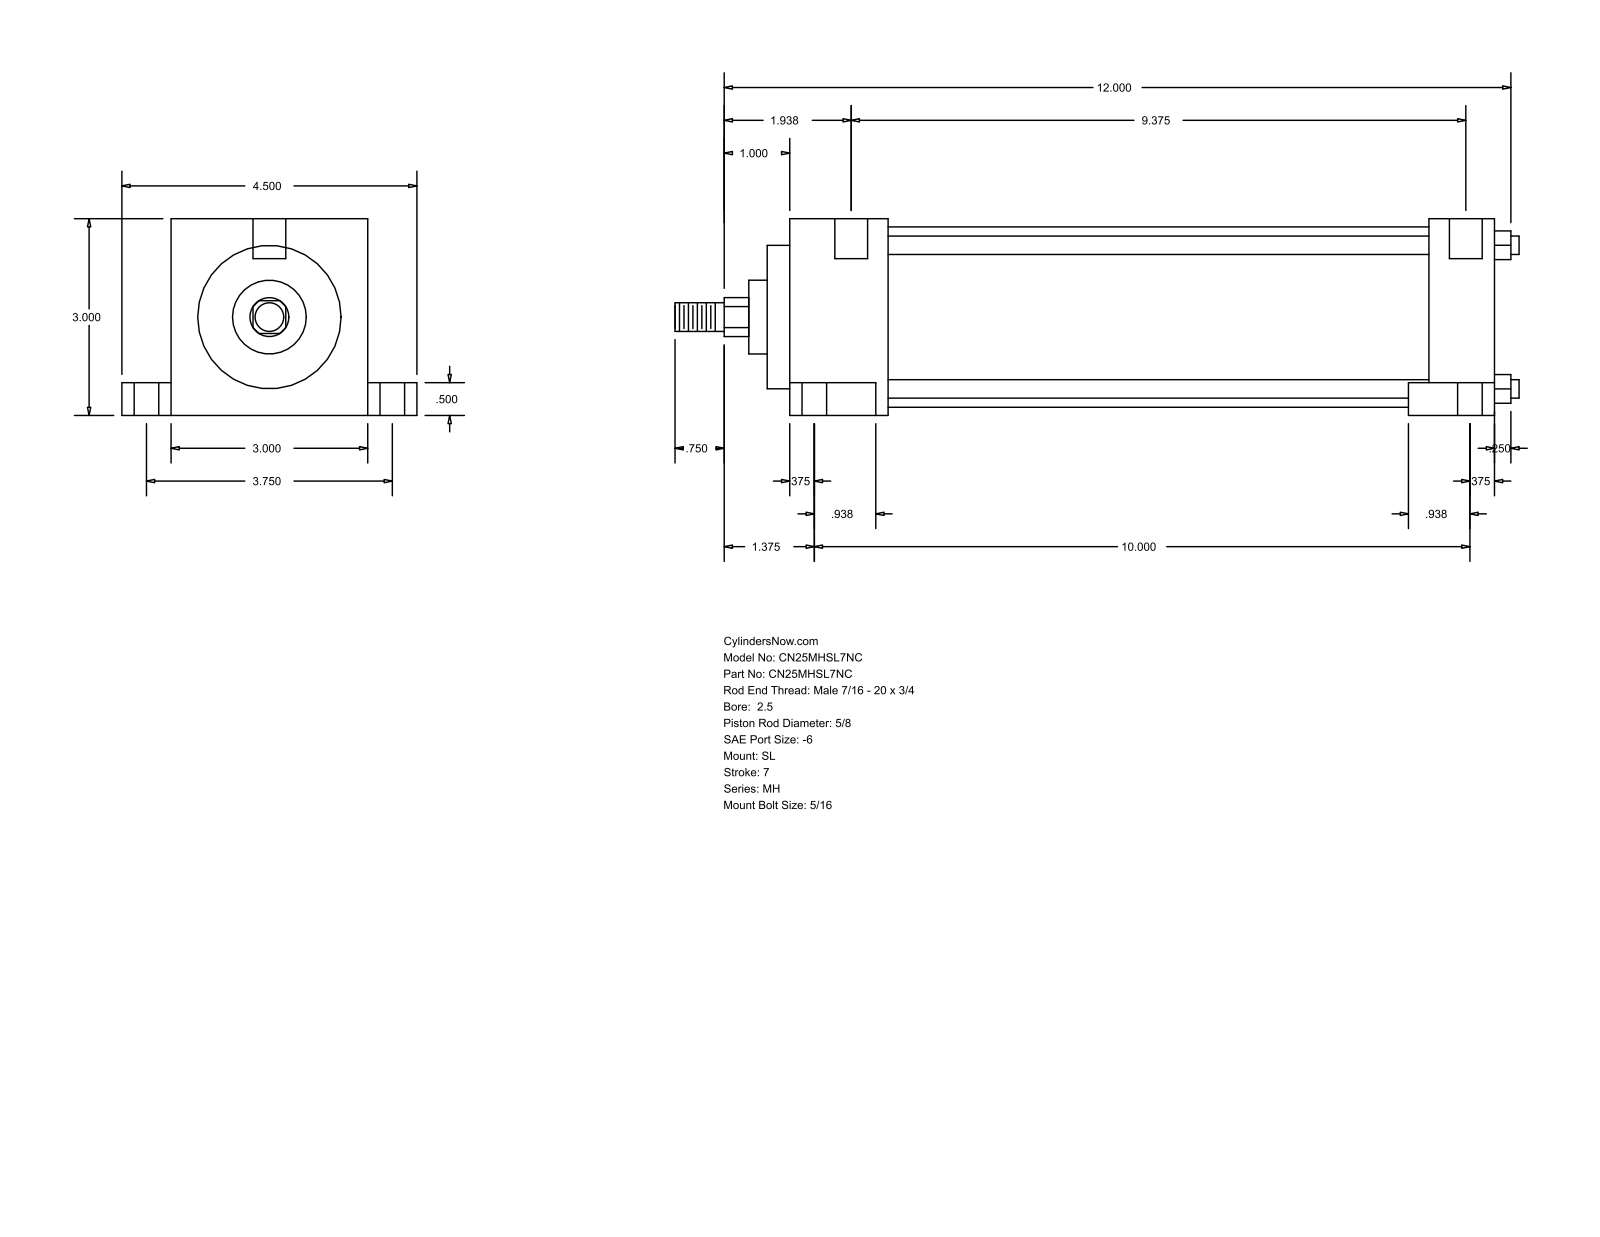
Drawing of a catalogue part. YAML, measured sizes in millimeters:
part_name: "MH_SL__0250_0.625"
step_written_by: "GSSL Pune (CONFIG_CONTROL_DESIGN)"
units: millimeters
bodies: {solids: 0, faces: 86, planar: 61, cylindrical: 25, other: 0}
overall_size: [327.02, 114.3, 76.2]
round_holes:
  - {diameter: 5.56, count: 2}
  - {diameter: 9.53, count: 2}
  - {diameter: 15.88, count: 2}
  - {diameter: 12.7, count: 1}
round_bosses_or_shafts:
  - {diameter: 7.14, count: 4}
  - {diameter: 69.85, count: 1}
  - {diameter: 55.55, count: 1}
  - {diameter: 28.57, count: 1}
  - {diameter: 15.88, count: 1}
  - {diameter: 11.11, count: 1}
partial_cylinders:
  - {radius: 7.54, count: 1}
face_to_face_distances: [76.2, 25.4, 256.38, 281.78, 63.5, 12.7, 19.05, 95.25, 31.75, 248.44]
hole_center_spacings: [47.65, 3.17, 95.24]
